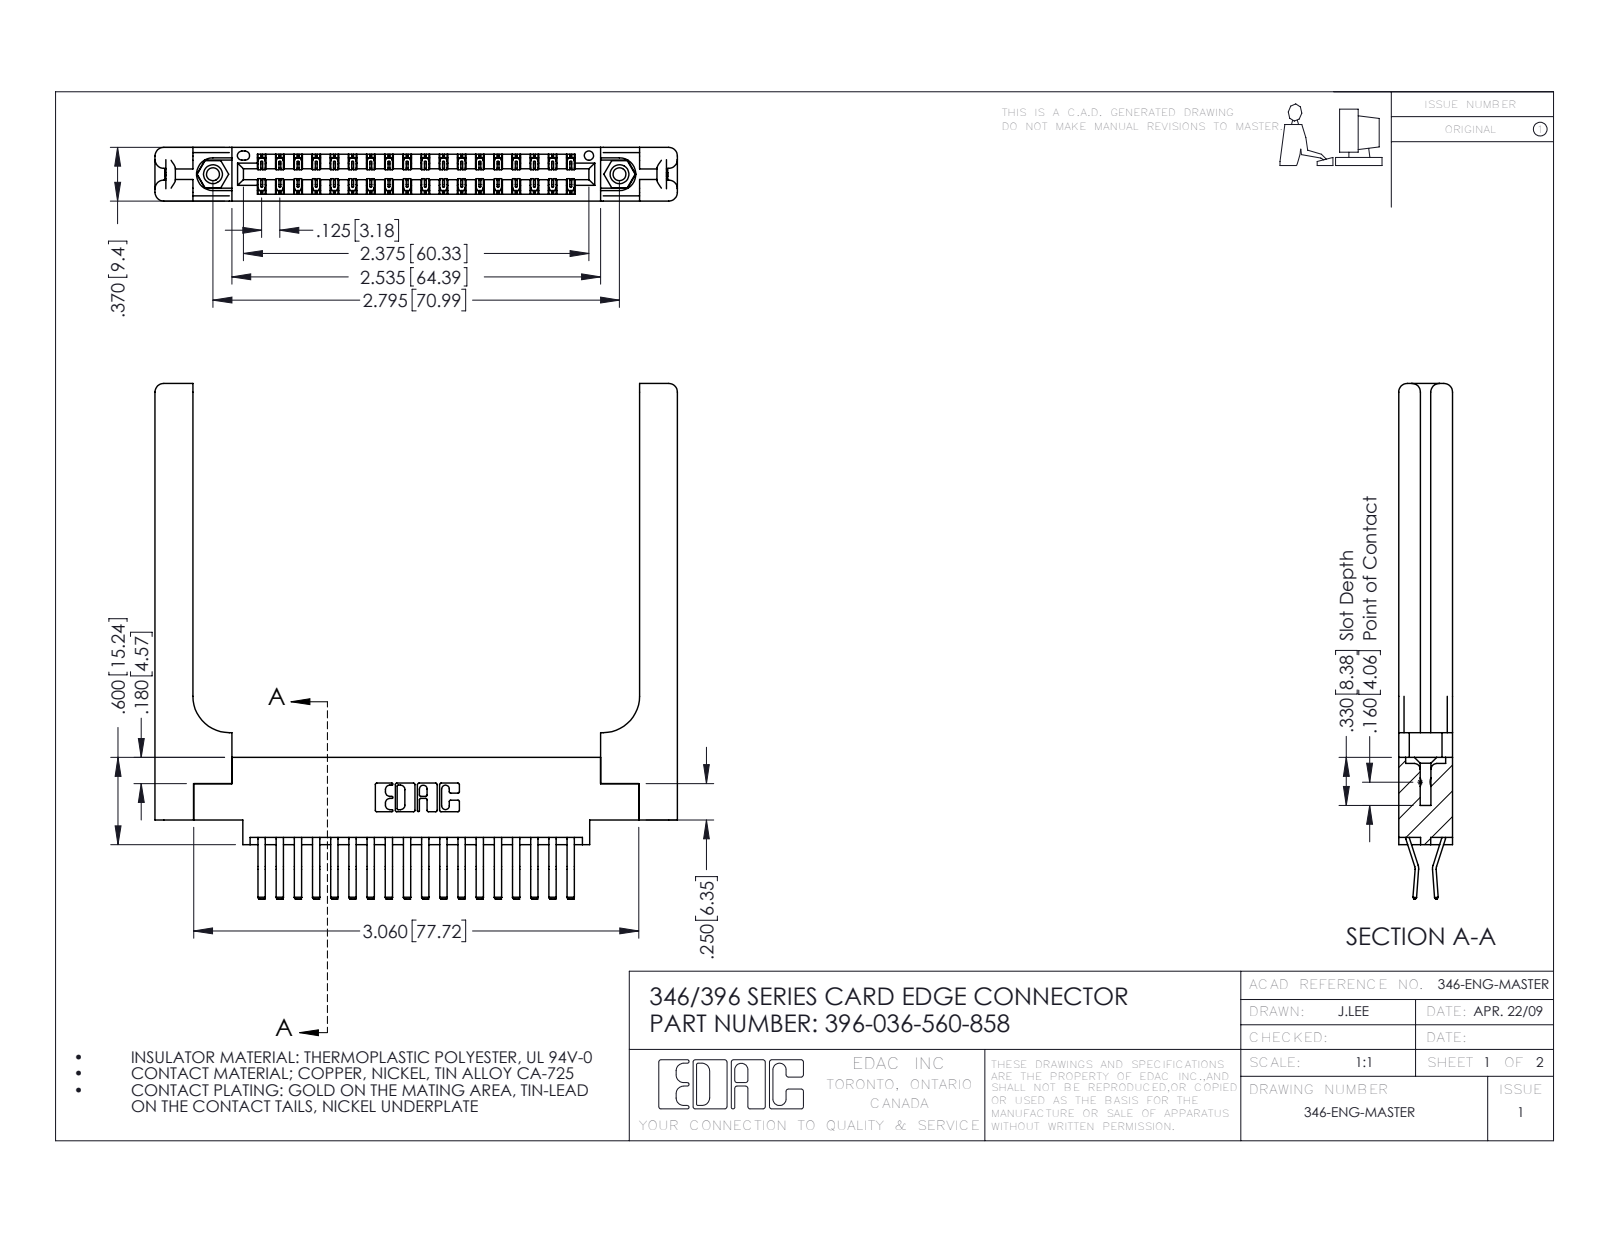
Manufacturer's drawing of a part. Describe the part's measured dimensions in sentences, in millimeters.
The part is named "345-292-001_560 Tail; 346-220-058_345-220-058; 396-036-560-858; 345-250-001_345-250-001-102 (+1 more)". Its 3-D file was written by "SolidWorks 2016 (CONFIG_CONTROL_DESIGN)". It is 41 solids with 2326 faces: 1488 planar, 778 cylindrical and 60 other. Overall it measures 91.2 by 90 by 9.4 millimeters. Its volume is 16 300 cubic millimeters and its surface area 17 480 square millimeters. Round holes: 2 of diameter 2.3, 2 of diameter 3.2, 2 of diameter 4, 1 of diameter 1.6. Round bosses or shafts: 2 of diameter 3.9. Partial cylindrical surfaces (rounded edges, fillets, slot ends): 54 of radius 0.2, 22 of radius 0.3, 16 of radius 1.5, 6 of radius 0.2, 6 of radius 0.8, 3 of radius 0.7, 2 of radius 0.3, 2 of radius 0.4. The main face-to-face distances are 9.4, 3.8, 1.8, 3.8, 1.2, 8.2, 0.6, 6.4, 2.6, 5.6. The hole center spacings are 6.2, 65.7, 71.
